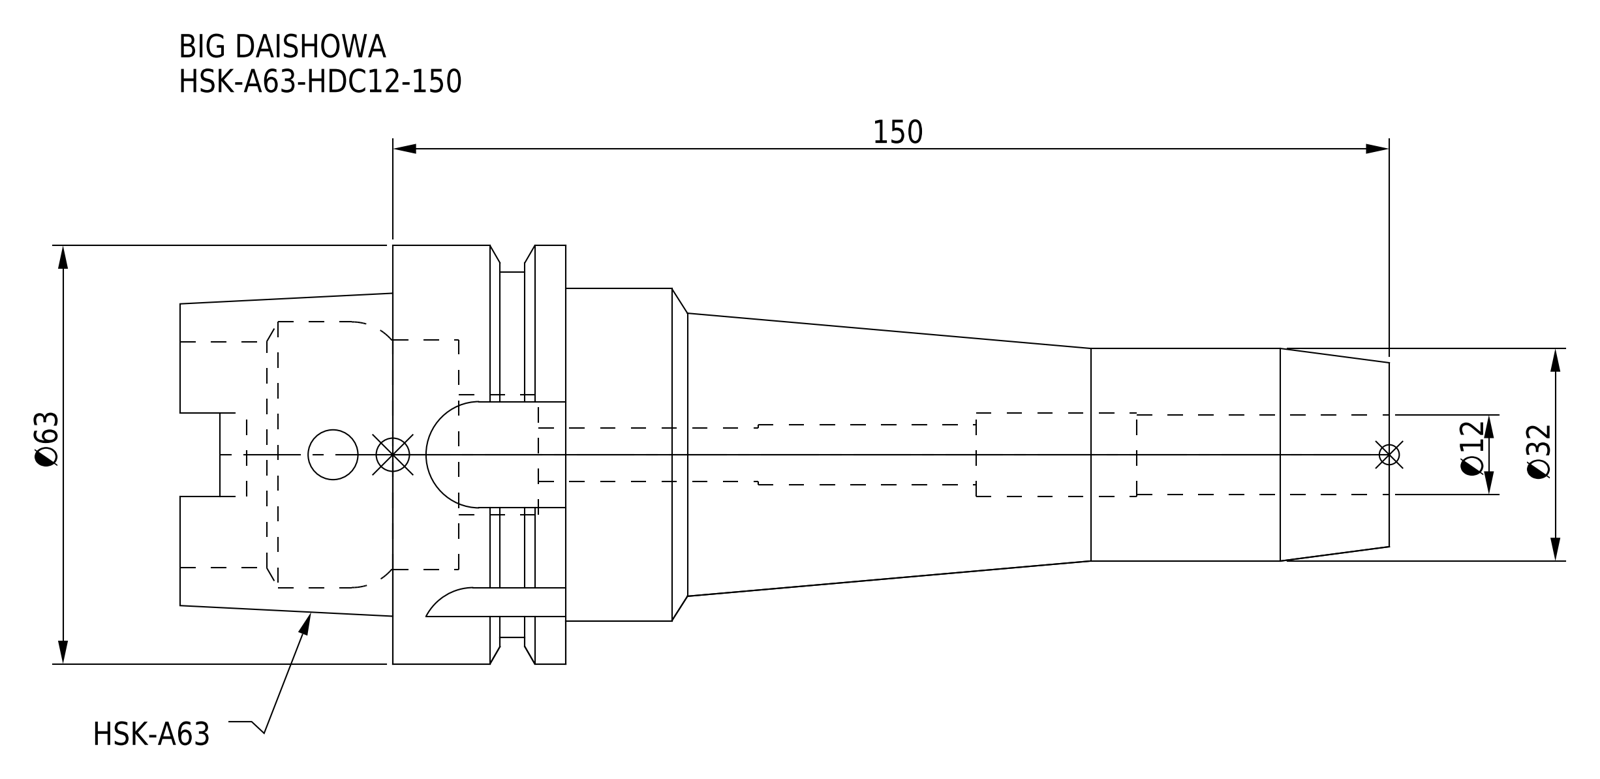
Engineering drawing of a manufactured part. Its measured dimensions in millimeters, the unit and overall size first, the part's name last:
Units: millimetres
Overall size (bounding box): 182 × 63 × 63
Round holes (diameter × count): ⌀7.5 ×1, ⌀8 ×1, ⌀9 ×1, ⌀12 ×1, ⌀12.5 ×1, ⌀18 ×1, ⌀34 ×1, ⌀34.5 ×1, ⌀40 ×1
Round bosses / shafts (diameter × count): ⌀63 ×1, ⌀55 ×1, ⌀50 ×1, ⌀32 ×1
Partial cylindrical surfaces — rounded edges, fillets, slot ends (radius × count): R2.88 ×4, R8 ×4
Main face-to-face distances: 26, 16.05, 9.95, 124, 140.05, 150, 182, 58, 41.95, 32
Volume: 207 458 mm³ · Surface area: 39 728 mm²
Bodies: 1 solid, 100 faces (39 planar, 41 cylindrical, 20 other)
Part name (STEP PRODUCT): HSK-A63-HDC12-150
STEP written by: CREO PARAMETRIC BY PTC INC, 2016380 (AUTOMOTIVE_DESIGN)
